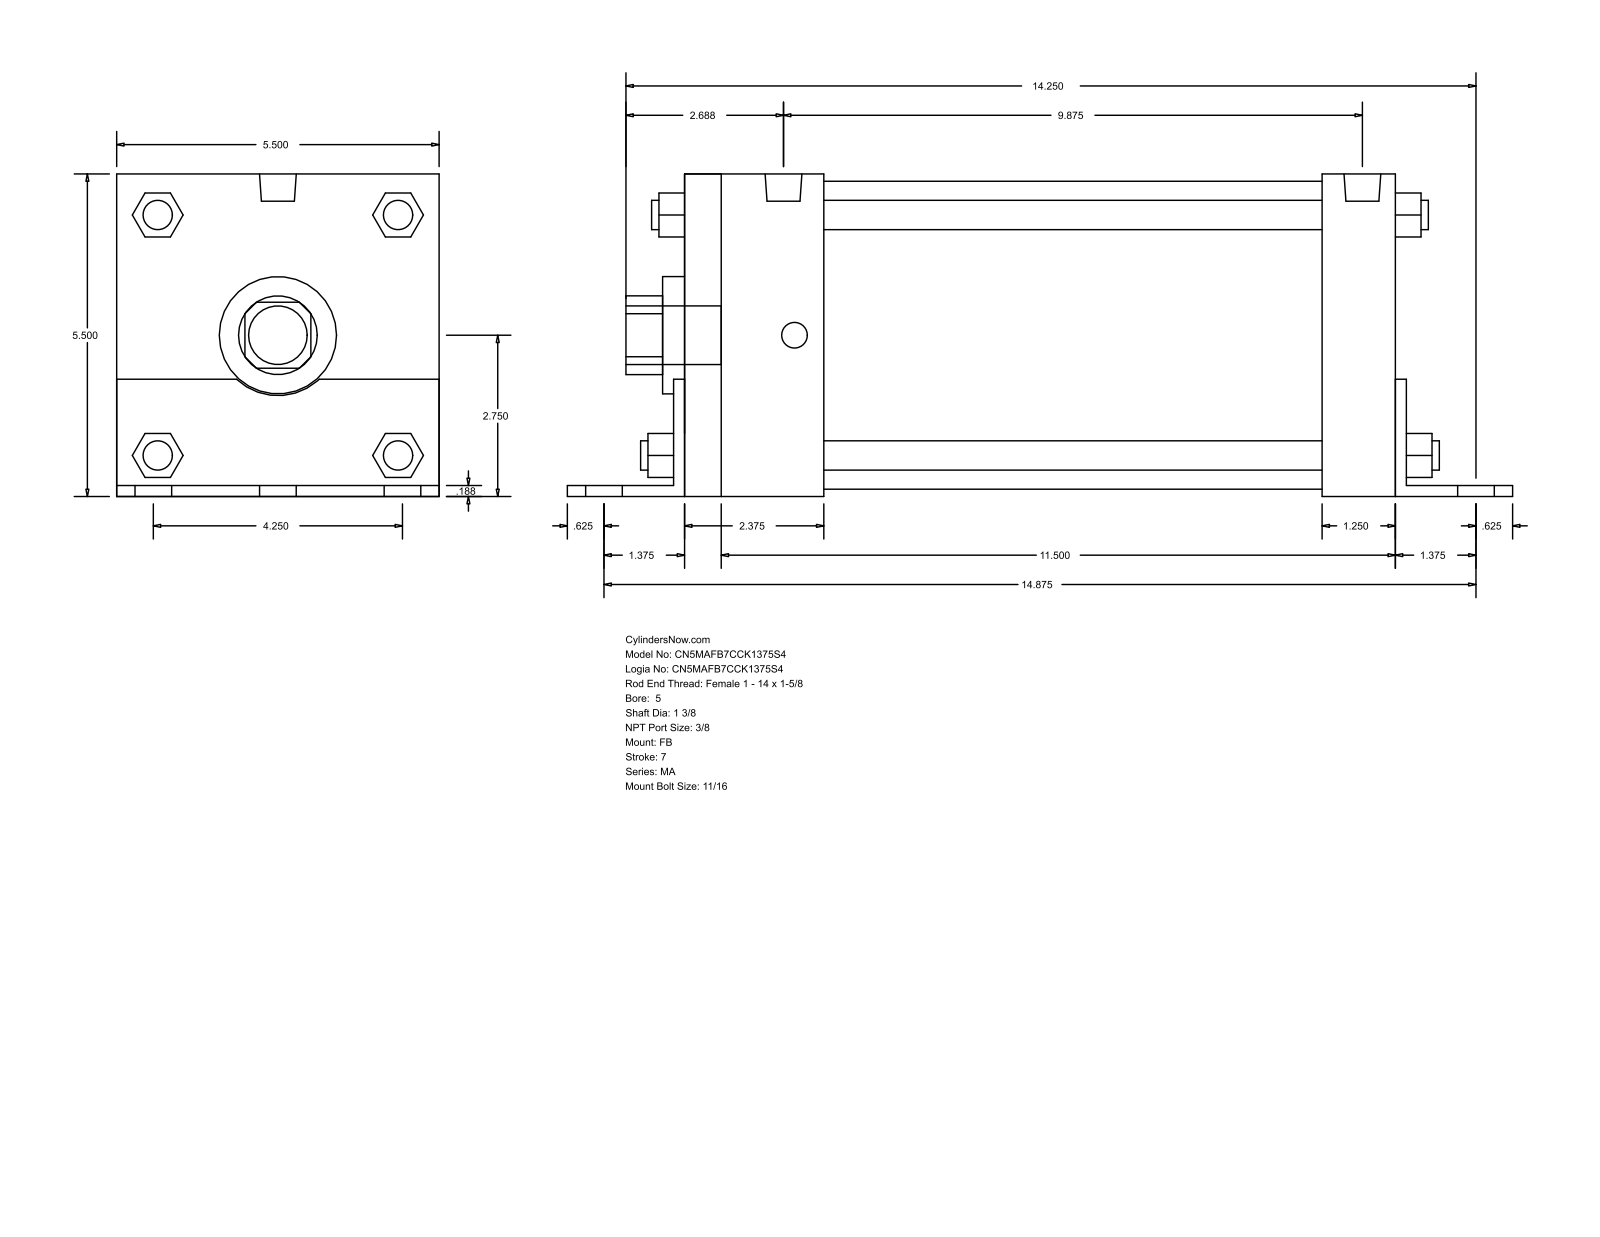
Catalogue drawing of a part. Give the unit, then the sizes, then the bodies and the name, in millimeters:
Units: millimetres
Overall size (bounding box): 409.57 × 139.75 × 139.7
Round holes (diameter × count): ⌀34.92 ×1, ⌀50.8 ×1, ⌀133.35 ×1
Round bosses / shafts (diameter × count): ⌀17.46 ×6, ⌀12.7 ×4, ⌀11.11 ×4, ⌀15.93 ×2, ⌀25.4 ×1
Partial cylindrical surfaces — rounded edges, fillets, slot ends (radius × count): R17.06 ×1, R26.16 ×1
Main face-to-face distances: 139.7, 4.76, 139.75, 312.74, 4.71, 134.99, 307.98, 317.5, 36.52, 65.08
Bodies: 0 solids, 140 faces (105 planar, 35 cylindrical, 0 other)
Part name (STEP PRODUCT): MA_FB__0500_1.375
STEP written by: GSSL Pune (CONFIG_CONTROL_DESIGN)
